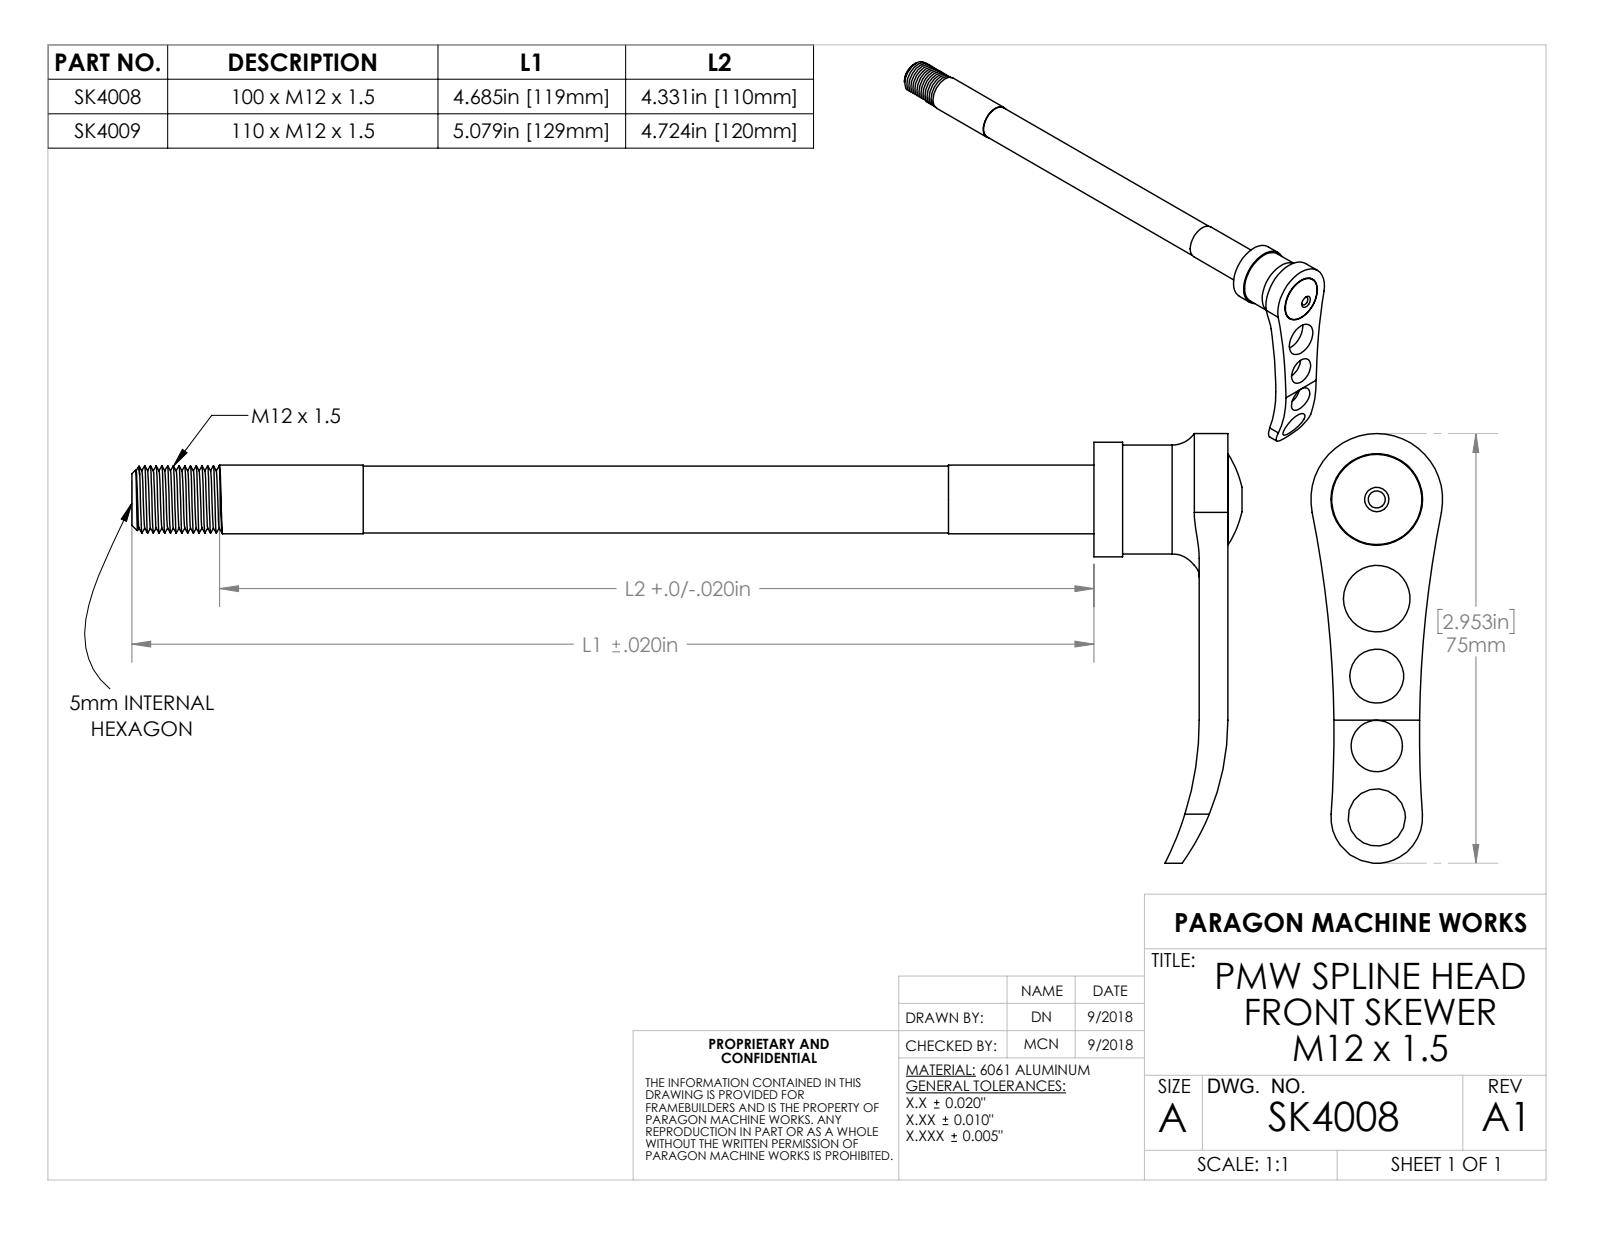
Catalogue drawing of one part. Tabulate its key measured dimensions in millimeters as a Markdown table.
| quantity | value |
| --- | --- |
| part name | SK4060_ROUND TOP; SK4061; SK40XX_100; SK4008 |
| STEP written by | SolidWorks 2023 (AUTOMOTIVE_DESIGN) |
| units | millimeters |
| bodies | 3 solids, 134 faces (28 planar, 67 cylindrical, 39 other) |
| overall size | 144.9 × 75 × 23 |
| volume | 21 830 mm³ |
| surface area | 11 660 mm² |
| round holes (diameter × count) | 3 × 1, 4.2 × 1, 9 × 1, 9.4 × 1, 10 × 1, 11.6 × 1, 13 × 1, 16 × 1 |
| round bosses / shafts (diameter × count) | 20 × 1, 19 × 1, 15.7 × 1, 12.4 × 1, 12 × 1, 11.7 × 1, 11.1 × 1, 10 × 1 |
| partial cylindrical surfaces (radius × count) | 1 × 10, 196.5 × 2, 8 × 1, 11.5 × 1, 43.1 × 1, 55.1 × 1 |
| main face-to-face distances | 18.4, 5, 13.4, 23.4, 22.1, 17.1, 3.7, 1.3, 10.5, 7.9 |
| hole center spacings | 12.2, 12.5, 13.5, 17.3, 24.7, 25.7, 30.8, 38.2 |
